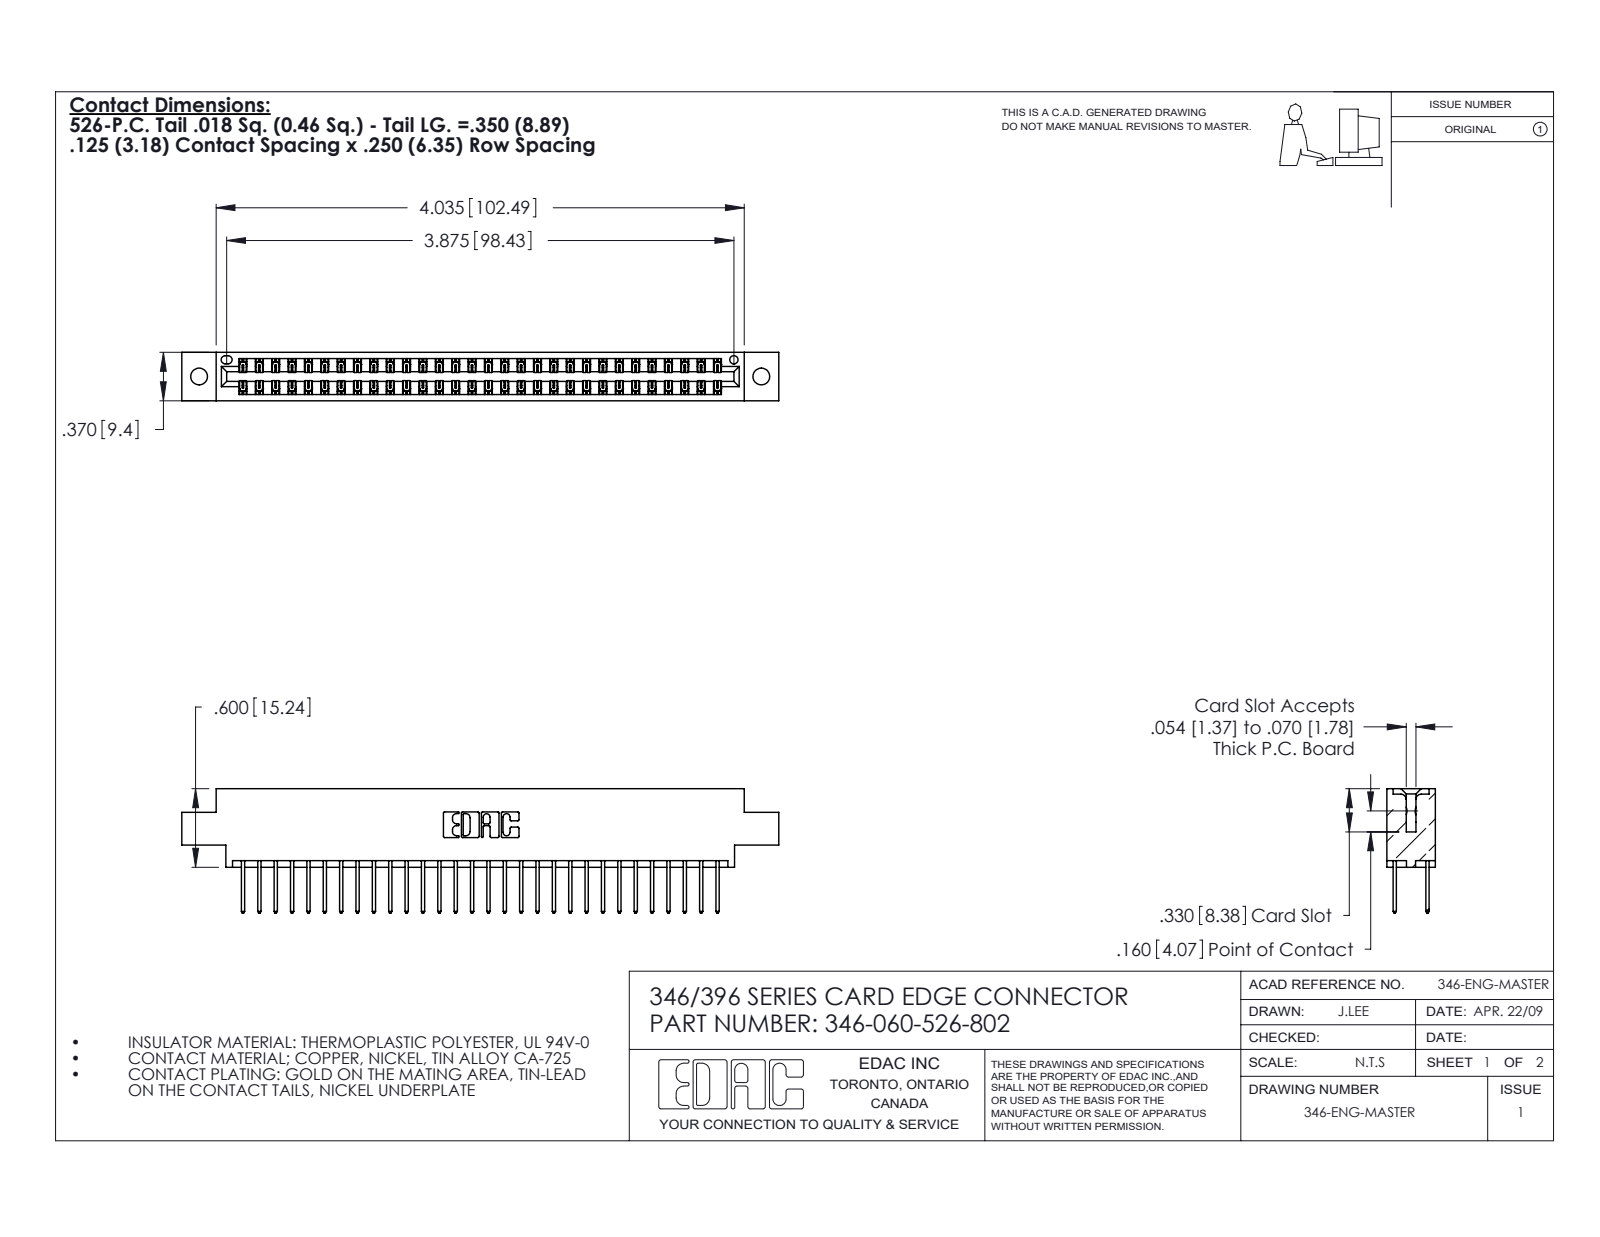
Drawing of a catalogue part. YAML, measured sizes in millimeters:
part_name: "345-292-001_345-293-126; 346-060-526-802; 346 Part_0.170 Offset - 0.128 Dia"
step_written_by: "SolidWorks 2020 (CONFIG_CONTROL_DESIGN)"
units: millimeters
bodies: {solids: 61, faces: 3246, planar: 2180, cylindrical: 1066, other: 0}
overall_size: [115.8, 24.1, 9.4]
volume: 11100
surface_area: 15430
round_holes:
  - {diameter: 3.3, count: 2}
  - {diameter: 1.6, count: 1}
partial_cylinders:
  - {radius: 0.2, count: 90}
  - {radius: 0.3, count: 60}
  - {radius: 0.3, count: 22}
  - {radius: 0.2, count: 6}
  - {radius: 0.8, count: 6}
  - {radius: 0.7, count: 3}
  - {radius: 0.4, count: 2}
  - {radius: 0.6, count: 2}
face_to_face_distances: [1.2, 8.2, 6.4, 9.4, 1.8, 7.6, 0.6, 7, 3.8, 5.6]
hole_center_spacings: [6.2, 103.8, 109.1]
